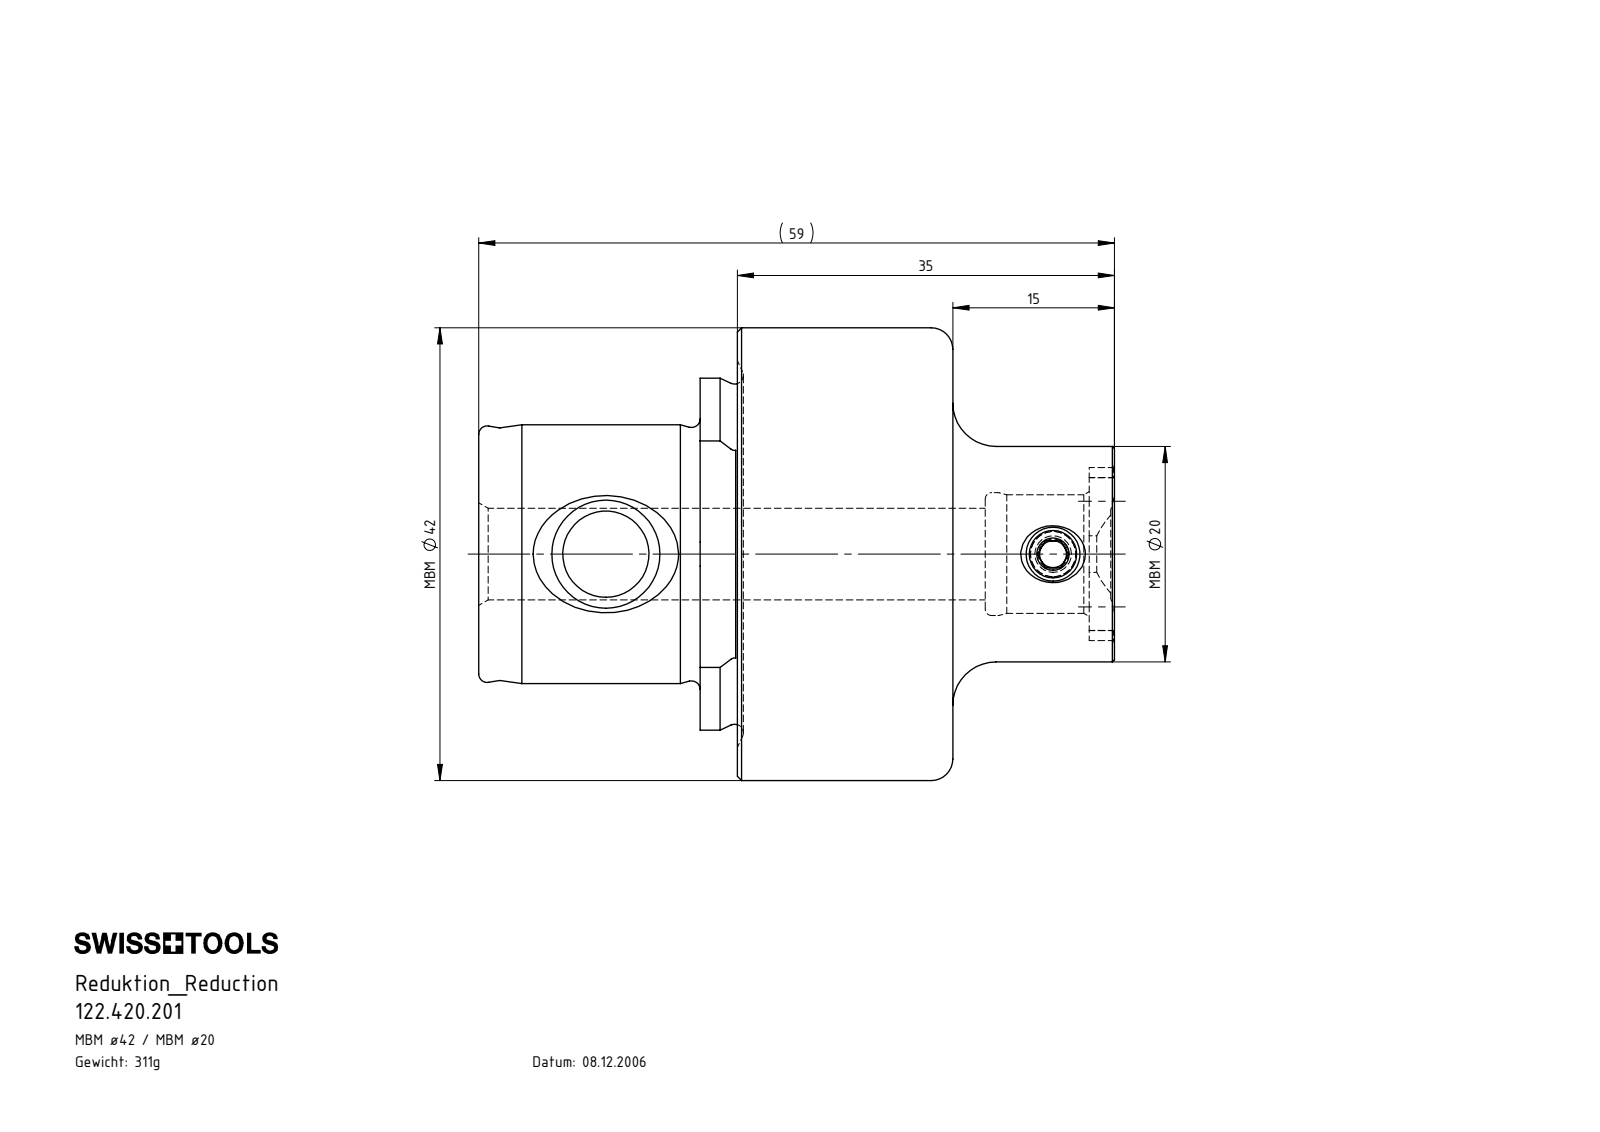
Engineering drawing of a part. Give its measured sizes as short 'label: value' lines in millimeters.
name: MB4-MB1.K01.035_C; MB1-ER1.001.006_A; 122.420.201
written by: SolidWorks 2017 (CONFIG_CONTROL_DESIGN)
unit: mm
bodies: 2 solids, 138 faces (34 planar, 34 cylindrical, 70 other)
size: 59 × 42 × 42
volume: 39 605 mm³; area: 9 825 mm²
holes: 1× ⌀2.5, 1× ⌀4.2, 1× ⌀8, 1× ⌀8.5, 1× ⌀11, 1× ⌀11.4
bosses: 1× ⌀42, 1× ⌀24, 1× ⌀20, 1× ⌀5
rounds: 4× R2.2, 1× R6.5, 1× R8.03, 1× R16.32
face distances: 20, 24, 44, 20.55, 3.45, 23.45, 23.85, 3.3, 20.15, 59
hole spacings: 41.5
